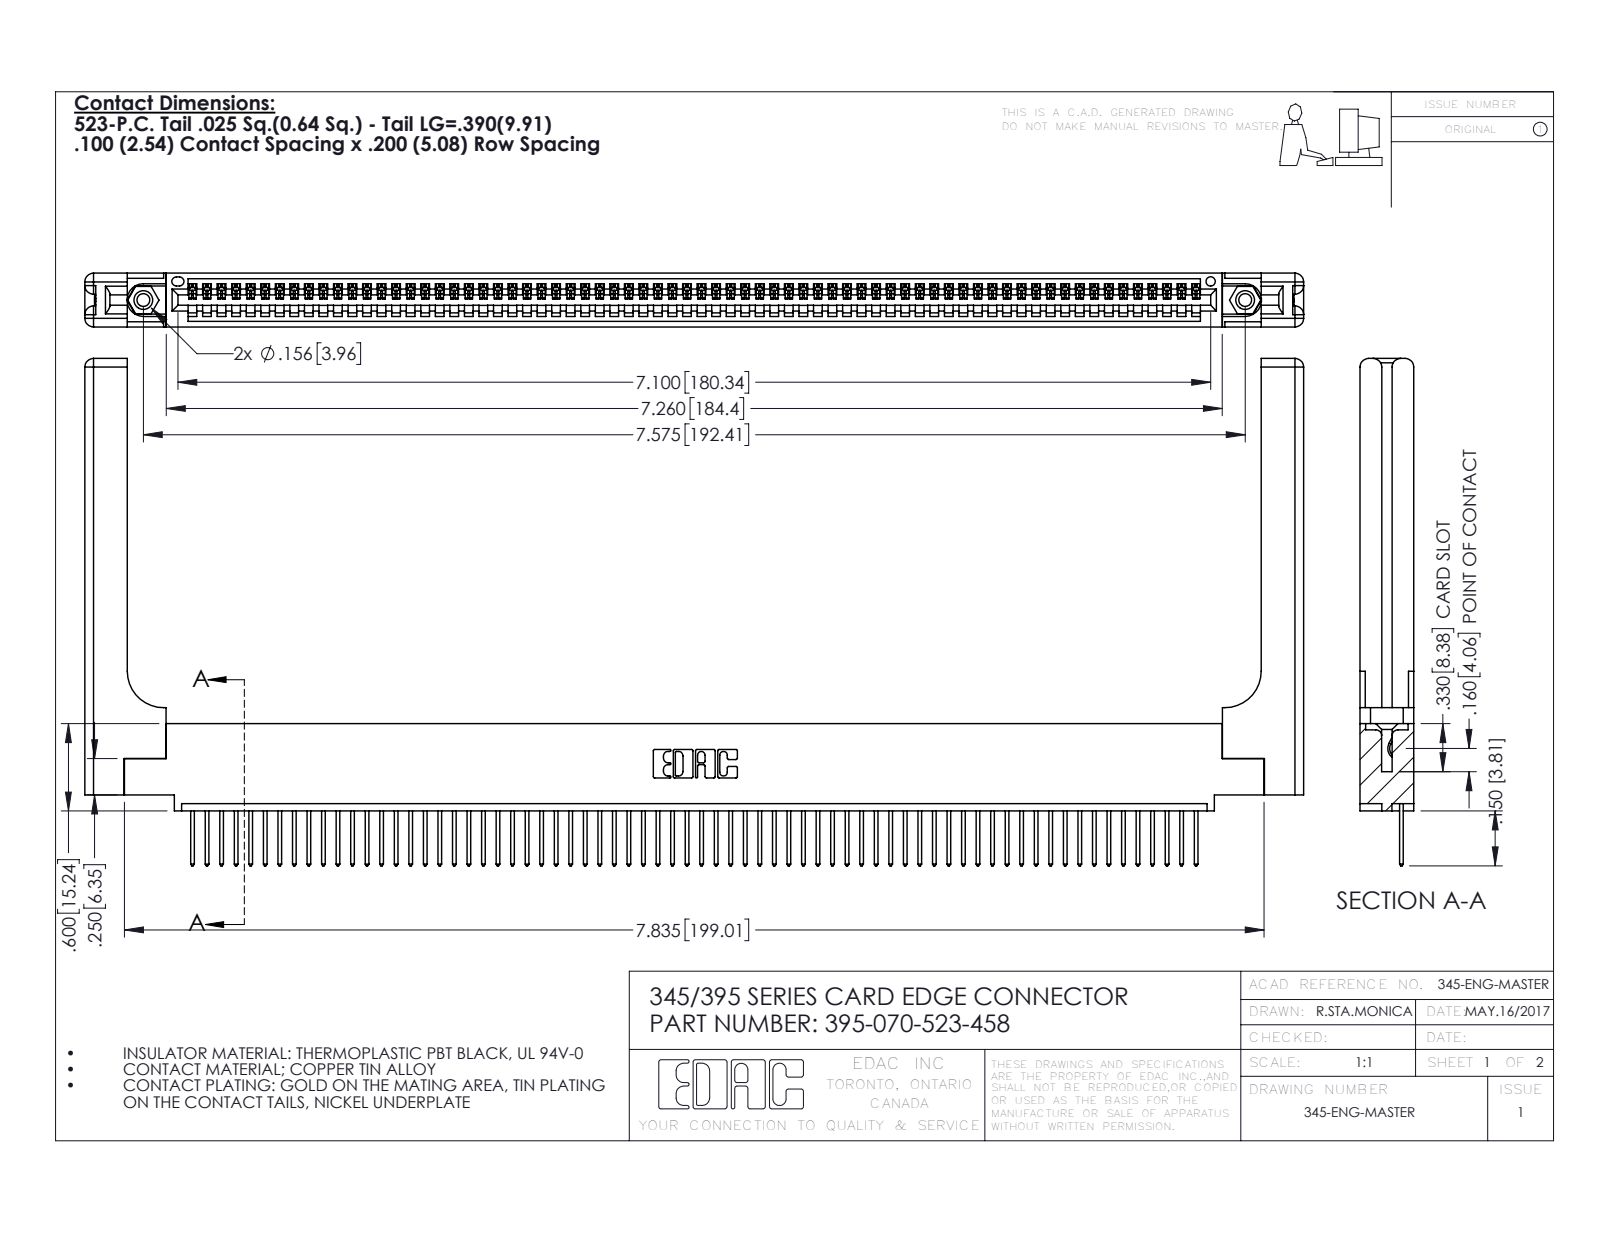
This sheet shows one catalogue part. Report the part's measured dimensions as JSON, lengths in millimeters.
{"part_name": "345-220-058_345-220-058; 395-070-523-458; 345 Part_0.110 Offset - 0.156 Dia-TH; 345-292-001_345-293-123 (+1 more)", "step_written_by": "SolidWorks 2016 (CONFIG_CONTROL_DESIGN)", "units": "millimeters", "bodies": {"solids": 75, "faces": 4446, "planar": 3032, "cylindrical": 1354, "other": 60}, "overall_size": [212.8, 88.6, 9.4], "volume_mm3": 28840, "surface_area_mm2": 32880, "round_holes": [[2.3, 2], [3.2, 2], [4, 2], [1.6, 1]], "round_bosses_or_shafts": [[3.9, 2]], "partial_cylinders_radius": [[0.2, 140], [0.3, 140], [0.3, 22], [1.5, 16], [0.2, 6], [0.8, 6], [0.7, 3], [0.8, 2]], "face_to_face_distances": [1.8, 7.6, 9.4, 2.5, 6.9, 0.6, 5.1, 5.7, 3.8, 3.8], "hole_center_spacings": [6.9, 186.4, 192.4]}
